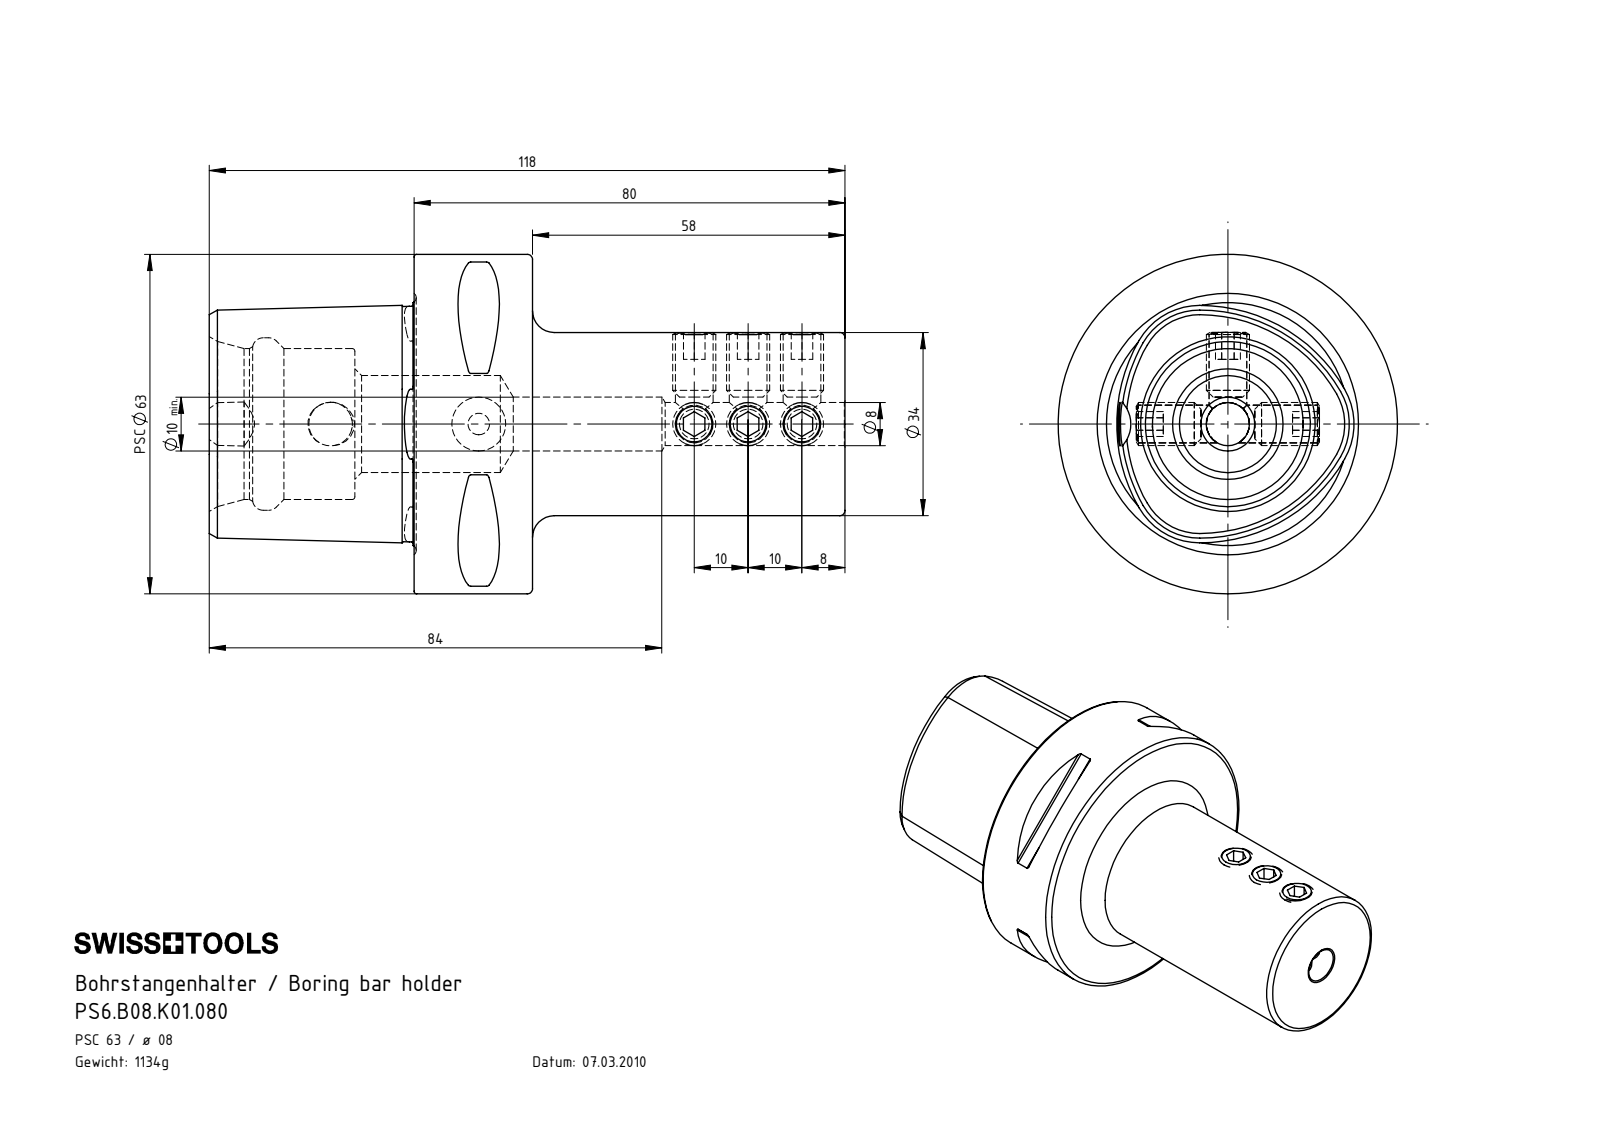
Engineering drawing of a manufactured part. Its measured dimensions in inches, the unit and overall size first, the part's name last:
Units: inches
Overall size (bounding box): 4.646 × 2.48 × 2.48
Round holes (diameter × count): ⌀0.276 ×6, ⌀0.157 ×1, ⌀0.315 ×1, ⌀0.319 ×1, ⌀0.394 ×1, ⌀0.709 ×1, ⌀1.102 ×1, ⌀1.26 ×1
Round bosses / shafts (diameter × count): ⌀0.315 ×6, ⌀2.48 ×1, ⌀1.339 ×1
Partial cylindrical surfaces — rounded edges, fillets, slot ends (radius × count): R0.02 ×8, R0.236 ×1
Main face-to-face distances: 0.866, 3.15, 2.283, 1.496, 2.362, 4.646, 0.197, 0.394, 0.157, 0.98
Hole centre spacings: 0.394, 0.787, 1.083, 1.575, 1.969, 2.362, 2.657, 3.051
Volume: 8.835 in³ · Surface area: 51.83 in²
Bodies: 10 solids, 288 faces (101 planar, 70 cylindrical, 117 other)
Part name (STEP PRODUCT): PS6.B08.K01.080; ISO 4026 - M8 x 12_PreviewCfg; PS6-B08.K01.080_A
STEP written by: SolidWorks 2017 (AUTOMOTIVE_DESIGN)
